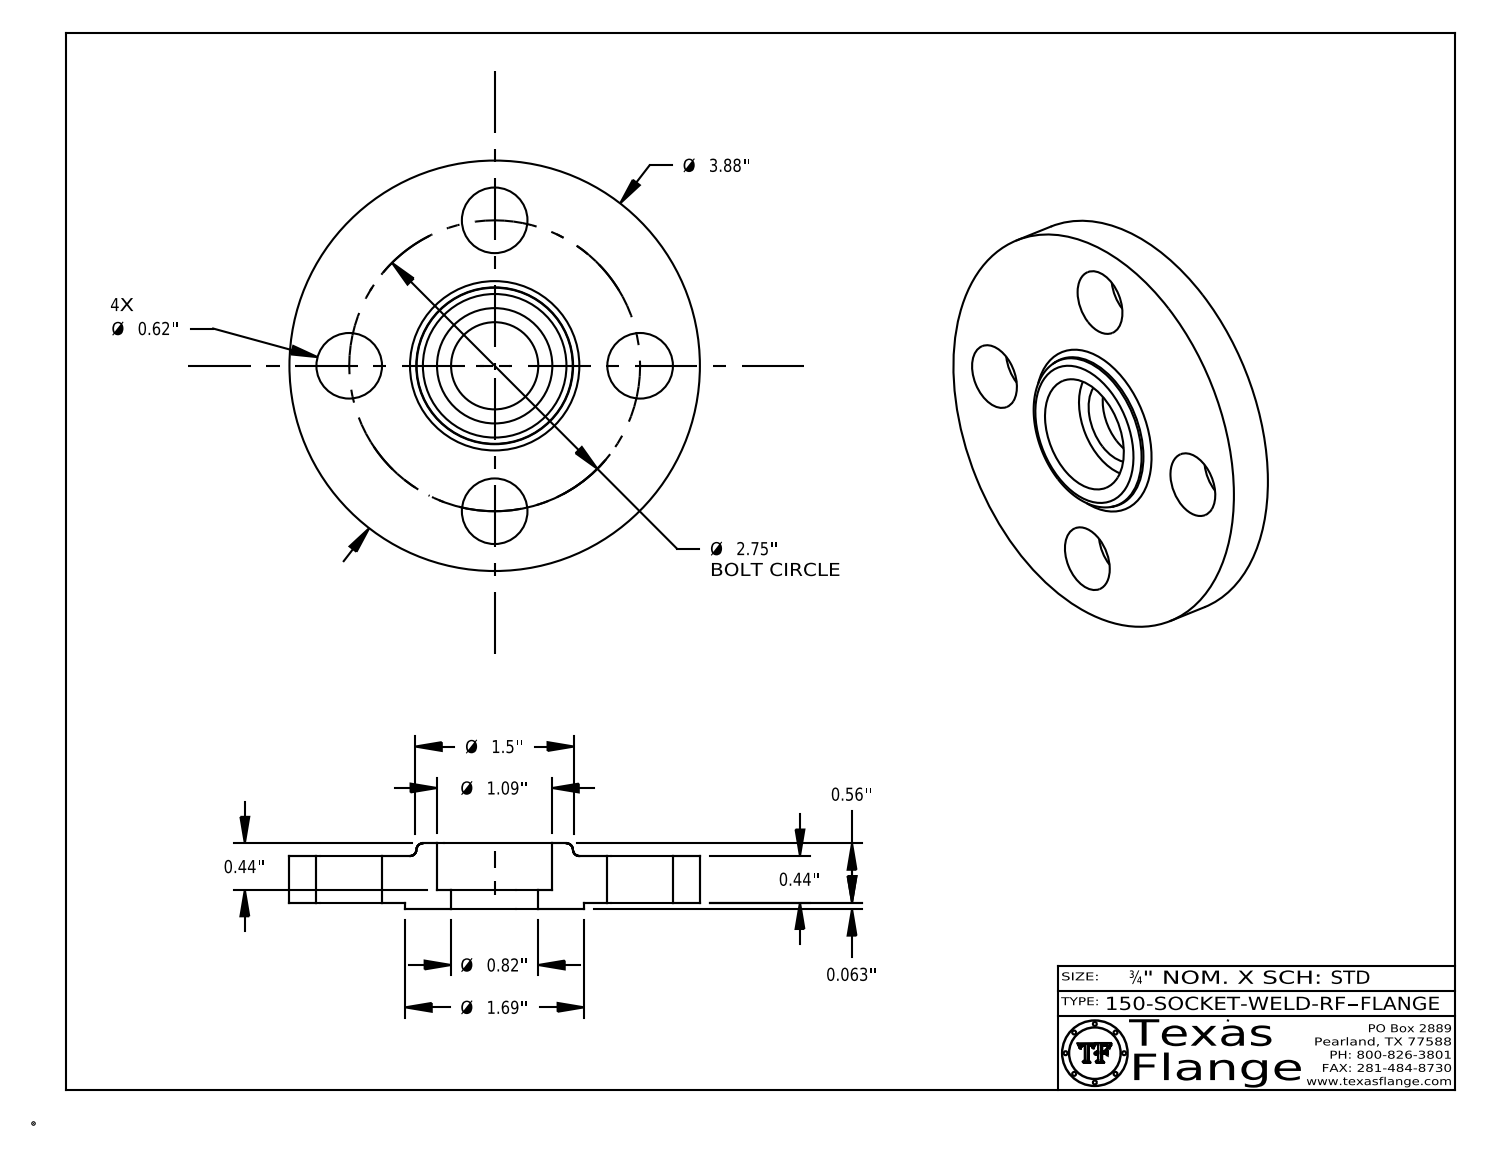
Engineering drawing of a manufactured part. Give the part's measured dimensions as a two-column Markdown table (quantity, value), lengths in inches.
| quantity | value |
| --- | --- |
| part name | 150-SOCKET-WELD-RF |
| STEP written by | CATIA V5 STEP AP214 (AUTOMOTIVE_DESIGN) |
| units | inches |
| bodies | 1 solid, 412 faces (370 planar, 36 cylindrical, 6 other) |
| overall size | 3.88 × 3.88 × 0.623 |
| volume | 4.508 in³ |
| surface area | 31.67 in² |
| round holes (diameter × count) | 0.62 × 4, 0.495 × 1, 0.824 × 1, 1.09 × 1 |
| round bosses / shafts (diameter × count) | 0.03 × 8, 3.88 × 1, 1.69 × 1, 0.39 × 1 |
| main face-to-face distances | 0.44, 0.063, 0.503, 0.622, 0.56, 0.12, 0.183, 0.12, 0.32, 0.44 |
| hole center spacings | 1.375, 1.945, 1.052, 2.541, 2.75 |
